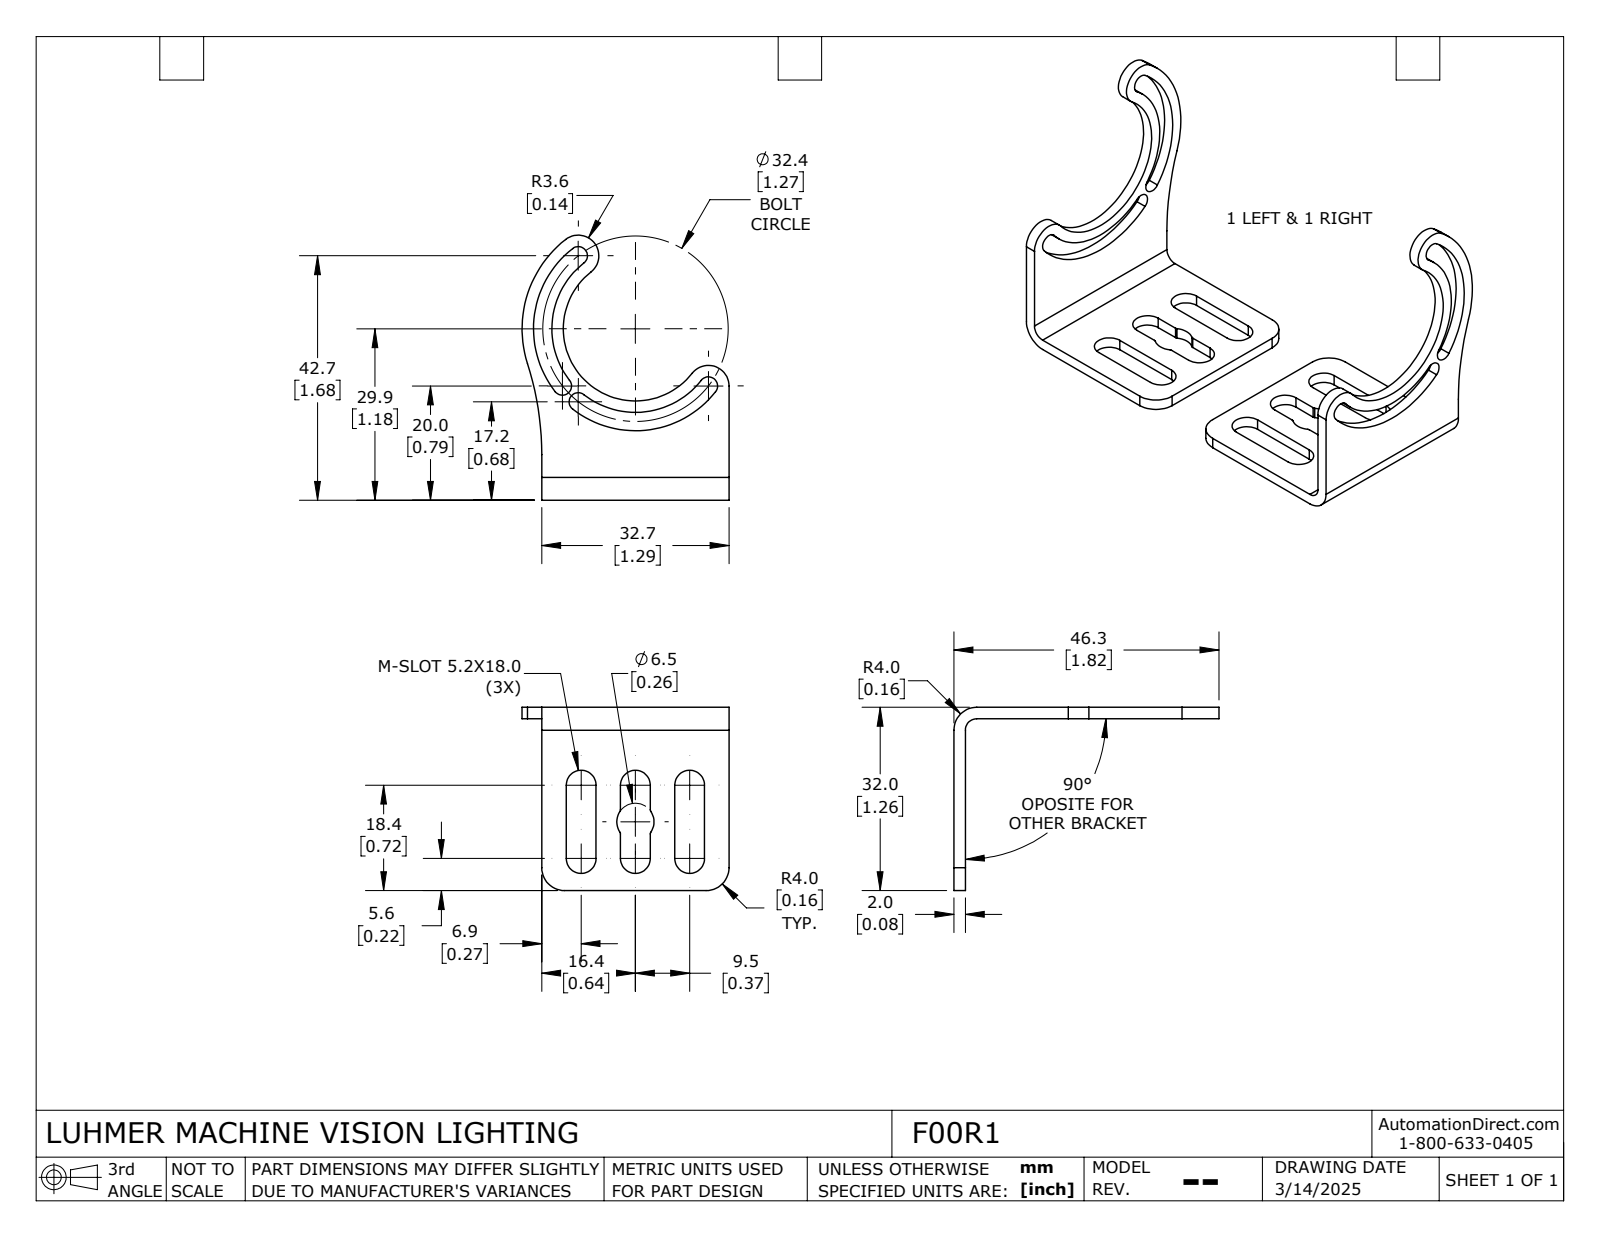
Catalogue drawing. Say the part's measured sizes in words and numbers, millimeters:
The part is named "F00R1". Its 3-D file was written by "SolidWorks 2024 (AUTOMOTIVE_DESIGN)". It is 2 solids with 88 faces: 30 planar, 58 cylindrical and 0 other. Overall it measures 74 by 46.28 by 36.14 millimeters. Its volume is 5 373 cubic millimeters and its surface area 7 237 square millimeters. Partial cylindrical surfaces (rounded edges, fillets, slot ends): 12 of radius 2.6, 8 of radius 0.5, 6 of radius 4, 4 of radius 1.6, 2 of radius 2, 2 of radius 3.25, 2 of radius 3.6, 1 of radius 12.59. The main face-to-face distances are 2, 72, 70, 74, 9.48, 32.7, 4.27, 5.2, 9.47, 28.43.
